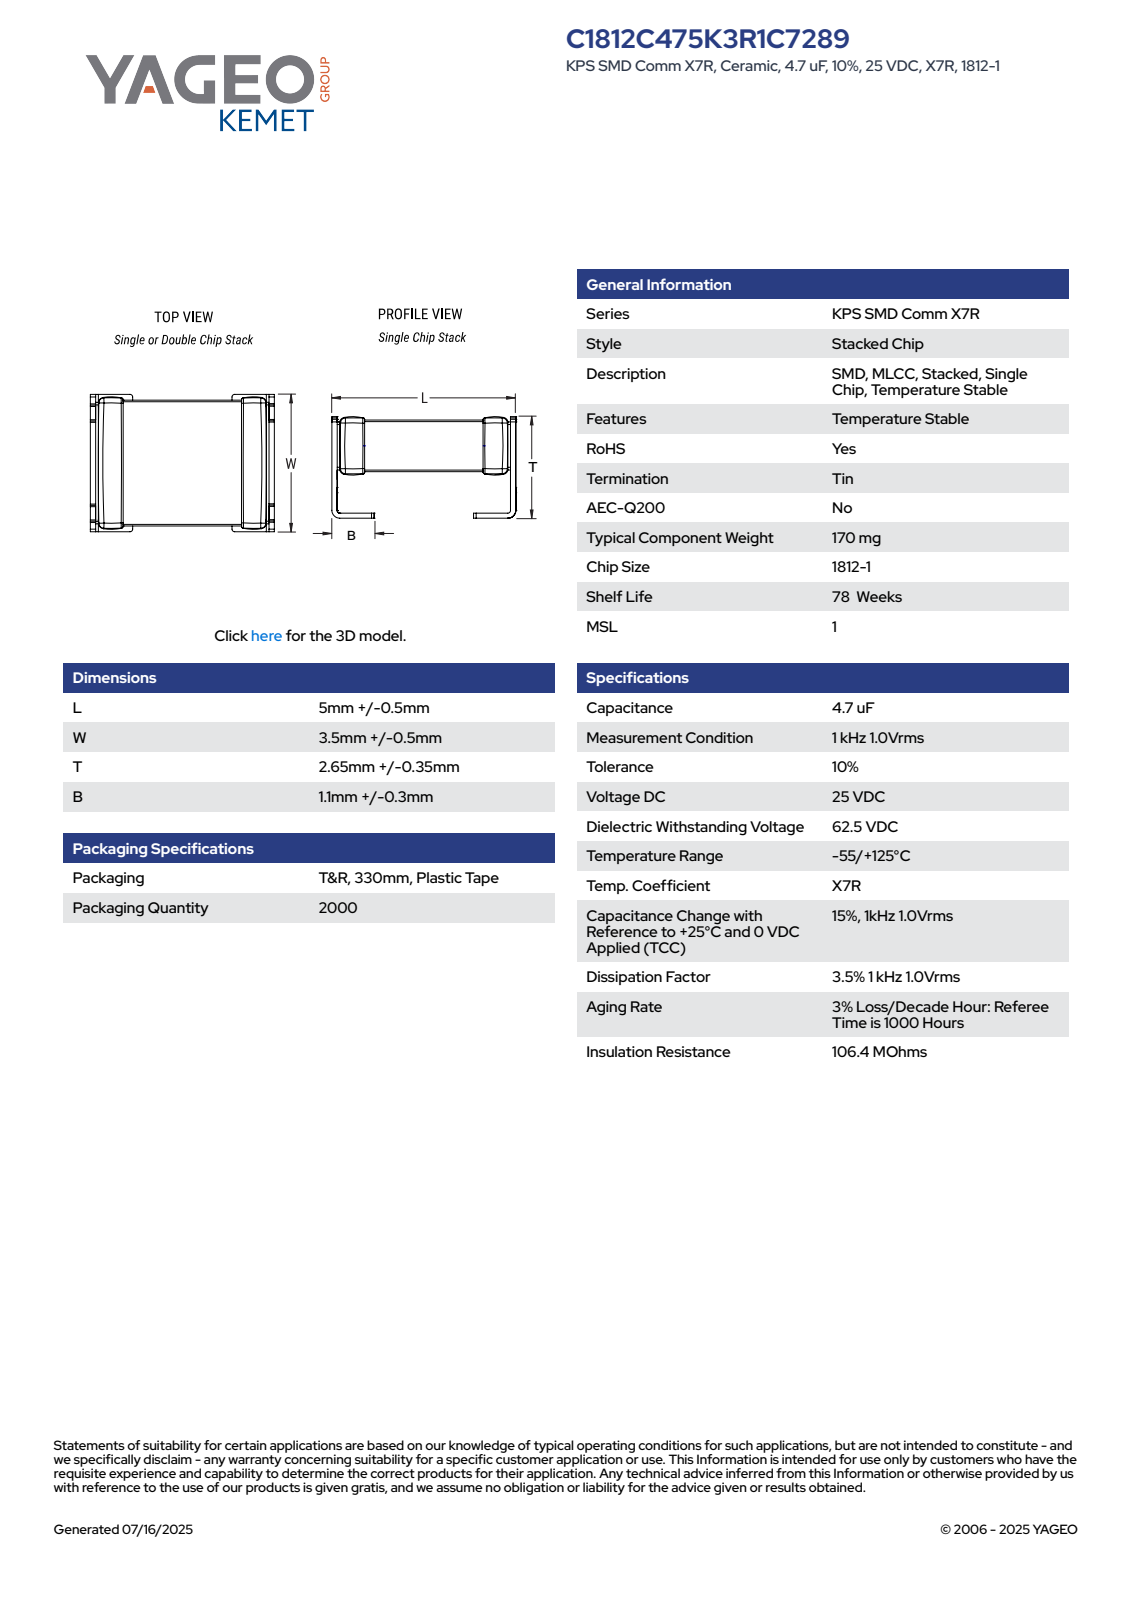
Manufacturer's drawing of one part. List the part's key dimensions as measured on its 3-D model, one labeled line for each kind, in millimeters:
Part name (STEP PRODUCT): CCSS_S1_1812-1_L5.5W4T3B1.4
STEP written by: SolidWorks 2021 (AUTOMOTIVE_DESIGN)
Units: millimetres
Bodies: 4 solids, 173 faces (105 planar, 56 cylindrical, 12 other)
Overall size (bounding box): 5.5 × 4 × 3
Volume: 27 mm³ · Surface area: 108 mm²
Main face-to-face distances: 1.17, 1.12, 2.95, 1.83, 1.73, 2.85, 2.9, 5.5, 3, 5.4
